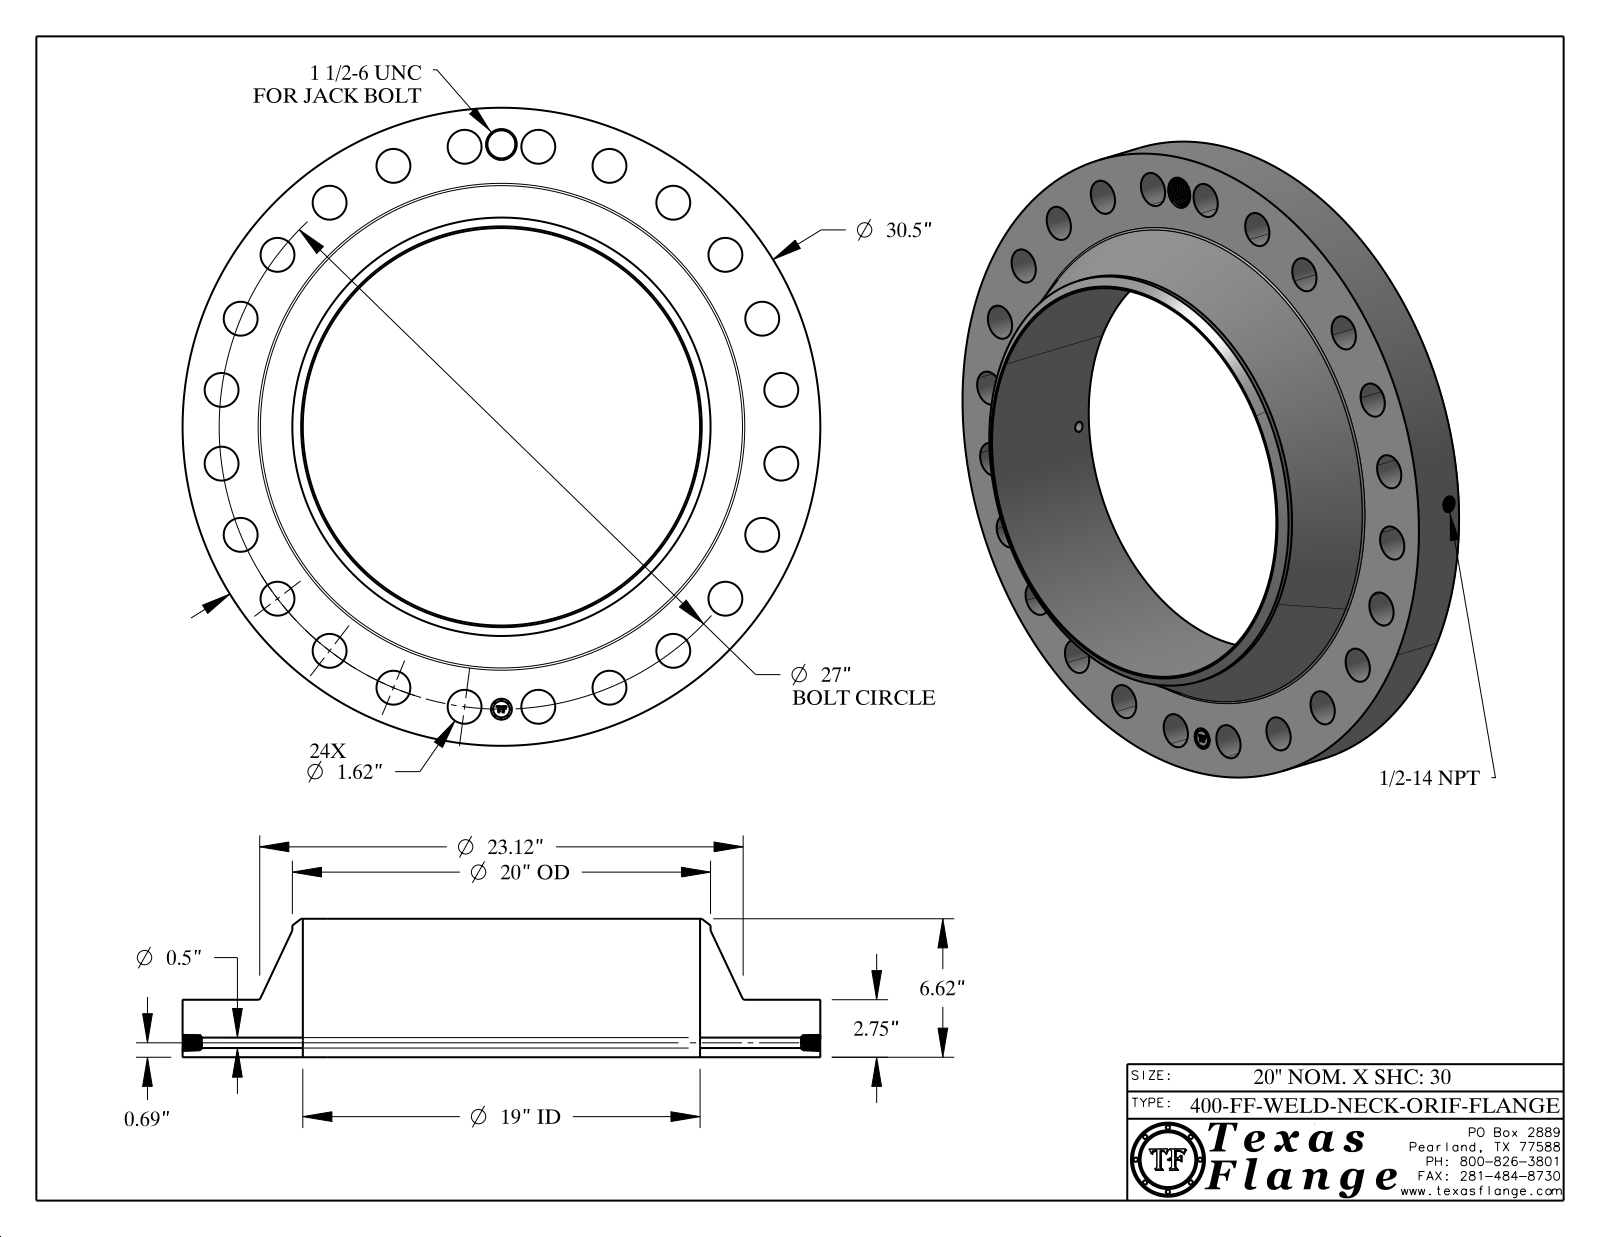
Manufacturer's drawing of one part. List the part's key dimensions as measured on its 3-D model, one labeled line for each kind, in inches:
Part name (STEP PRODUCT): 400-FF-WELD-NECK
STEP written by: CATIA V5 STEP AP214 (AUTOMOTIVE_DESIGN)
Units: inches
Bodies: 1 solid, 807 faces (368 planar, 127 cylindrical, 312 other)
Overall size (bounding box): 30.5 × 30.5 × 6.62
Volume: 1 371 in³ · Surface area: 1 988 in²
Round holes (diameter × count): ⌀1.62 ×24, ⌀0.5 ×1, ⌀0.672 ×1, ⌀1 ×1, ⌀1.344 ×1, ⌀19 ×1
Round bosses / shafts (diameter × count): ⌀0.061 ×8, ⌀30.5 ×1, ⌀20 ×1, ⌀0.788 ×1
Main face-to-face distances: 2.75, 6.62, 3.87, 2.735, 0.015, 3.885, 0.298, 0.293, 0.054, 0.248
Hole centre spacings: 13.5, 23.383, 24.945, 21.42, 3.524, 6.988, 19.092, 26.08
